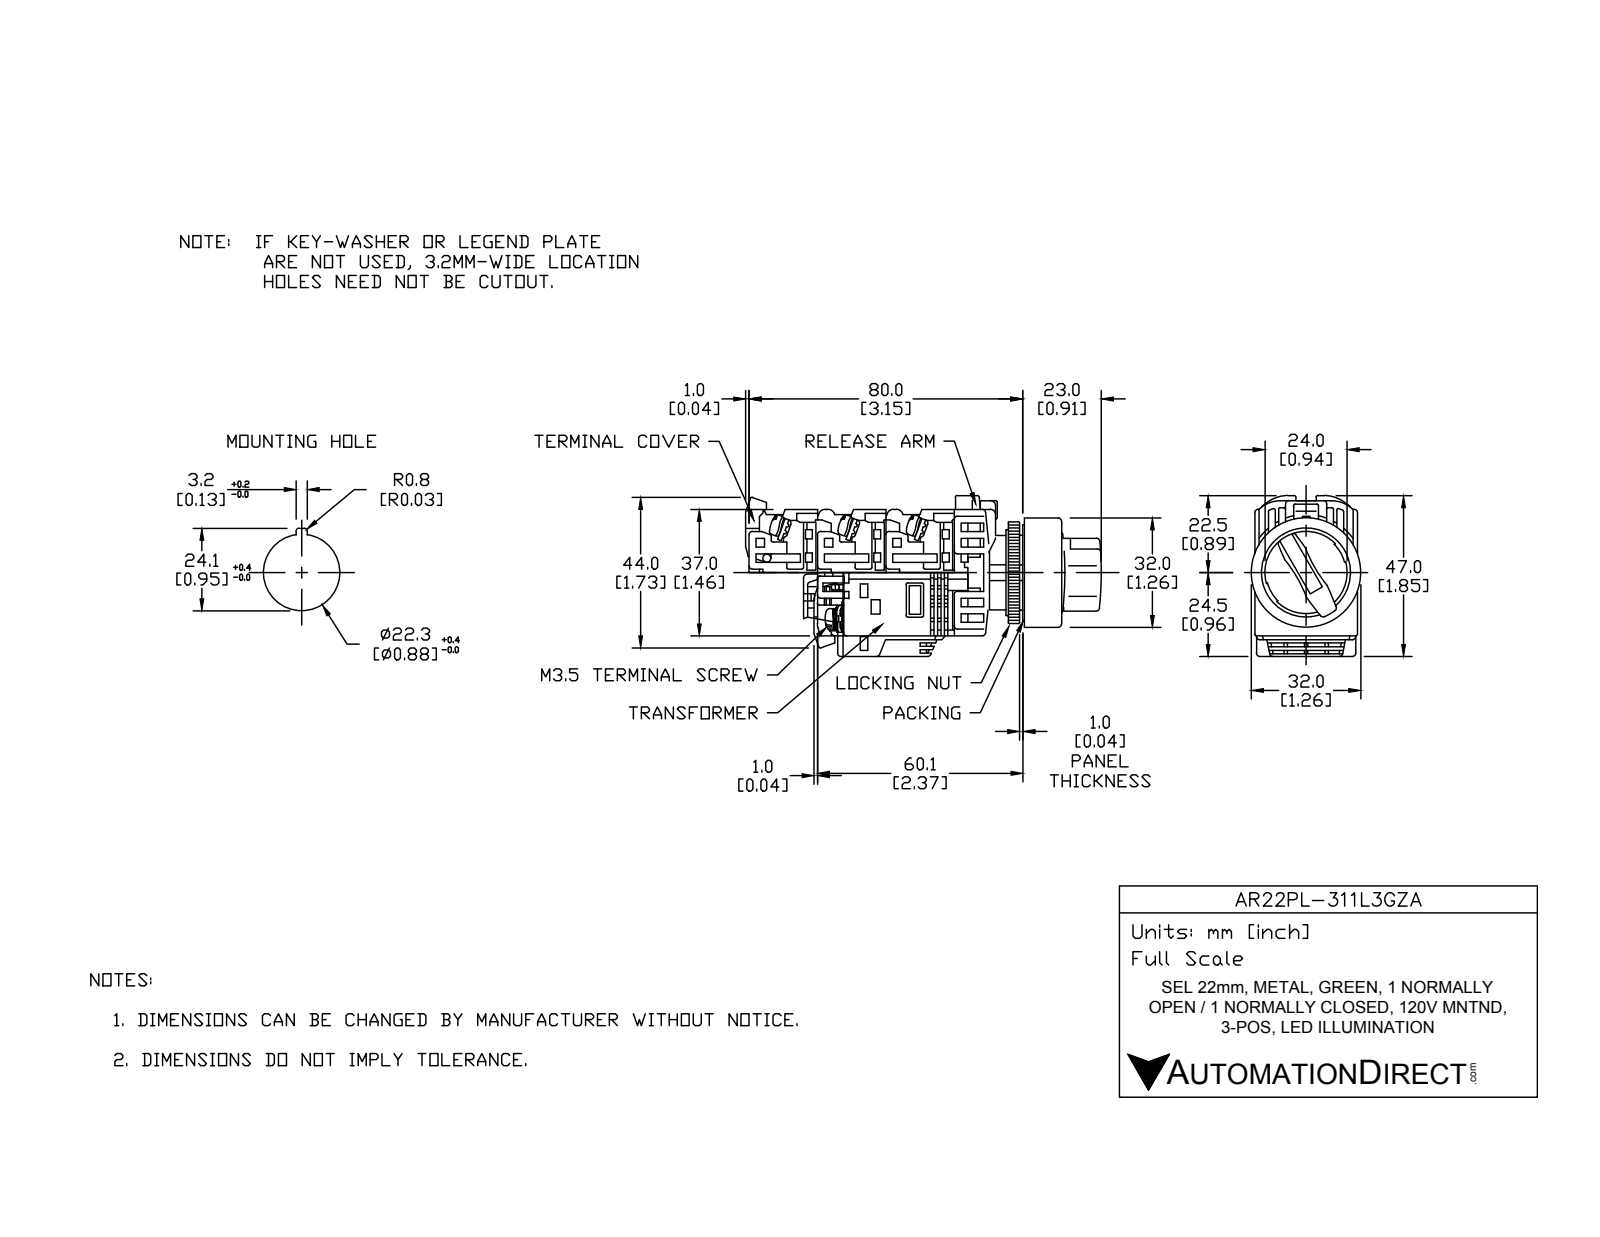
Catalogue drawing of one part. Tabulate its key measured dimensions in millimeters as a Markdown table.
| quantity | value |
| --- | --- |
| part name | AR22PL-311L3GZA |
| STEP written by | SolidWorks 2017 (AUTOMOTIVE_DESIGN) |
| units | millimeters |
| bodies | 24 solids, 602 faces (413 planar, 155 cylindrical, 34 other) |
| overall size | 84.5 × 43.81 × 32 |
| volume | 58 015 mm³ |
| surface area | 31 382 mm² |
| round holes (diameter × count) | 21.8 × 1, 22 × 1, 25 × 1, 31 × 1 |
| round bosses / shafts (diameter × count) | 5 × 6, 32 × 1, 30.5 × 1, 29.8 × 1, 24 × 1, 21.75 × 1, 17 × 1 |
| partial cylindrical surfaces (radius × count) | 0.5 × 55, 1.75 × 12, 1 × 6, 5 × 4, 4 × 2, 12 × 1, 16.59 × 1, 17.59 × 1 |
| main face-to-face distances | 1, 20, 18, 29, 3, 40, 28.5, 0.5, 68.5, 21 |
